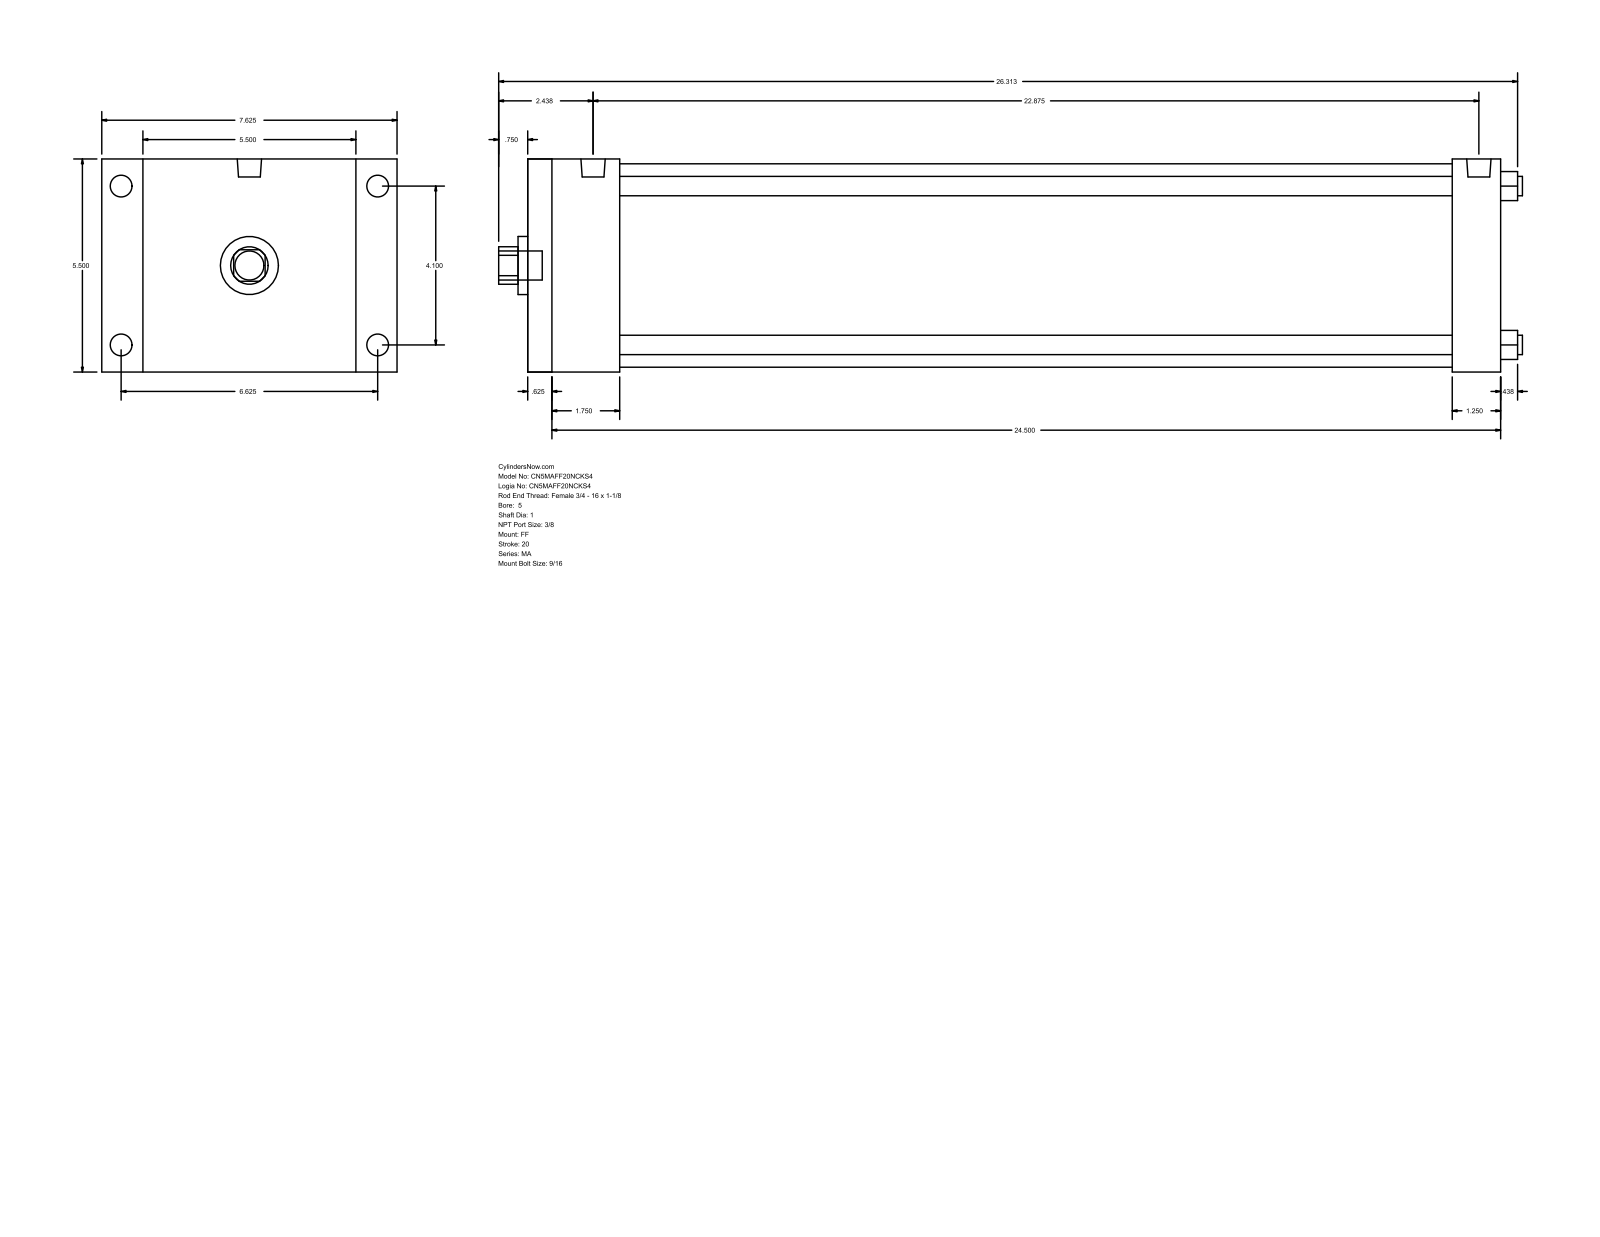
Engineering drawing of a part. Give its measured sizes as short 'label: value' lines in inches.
name: MA_FF__0500_1
written by: GSSL Pune (CONFIG_CONTROL_DESIGN)
unit: in
bodies: 0 solids, 92 faces (64 planar, 28 cylindrical, 0 other)
size: 26.437 × 7.625 × 5.5
holes: 4× ⌀0.5, 1× ⌀1, 1× ⌀1.5, 1× ⌀5.25
bosses: 4× ⌀0.563, 4× ⌀0.437, 2× ⌀0.627, 1× ⌀0.75
rounds: 1× R0.484
face distances: 5.5, 25.125, 0.625, 24.5, 23.875, 23.25, 1.25, 2.375, 1.75, 21.5
hole spacings: 2.899, 4.1, 5.798
